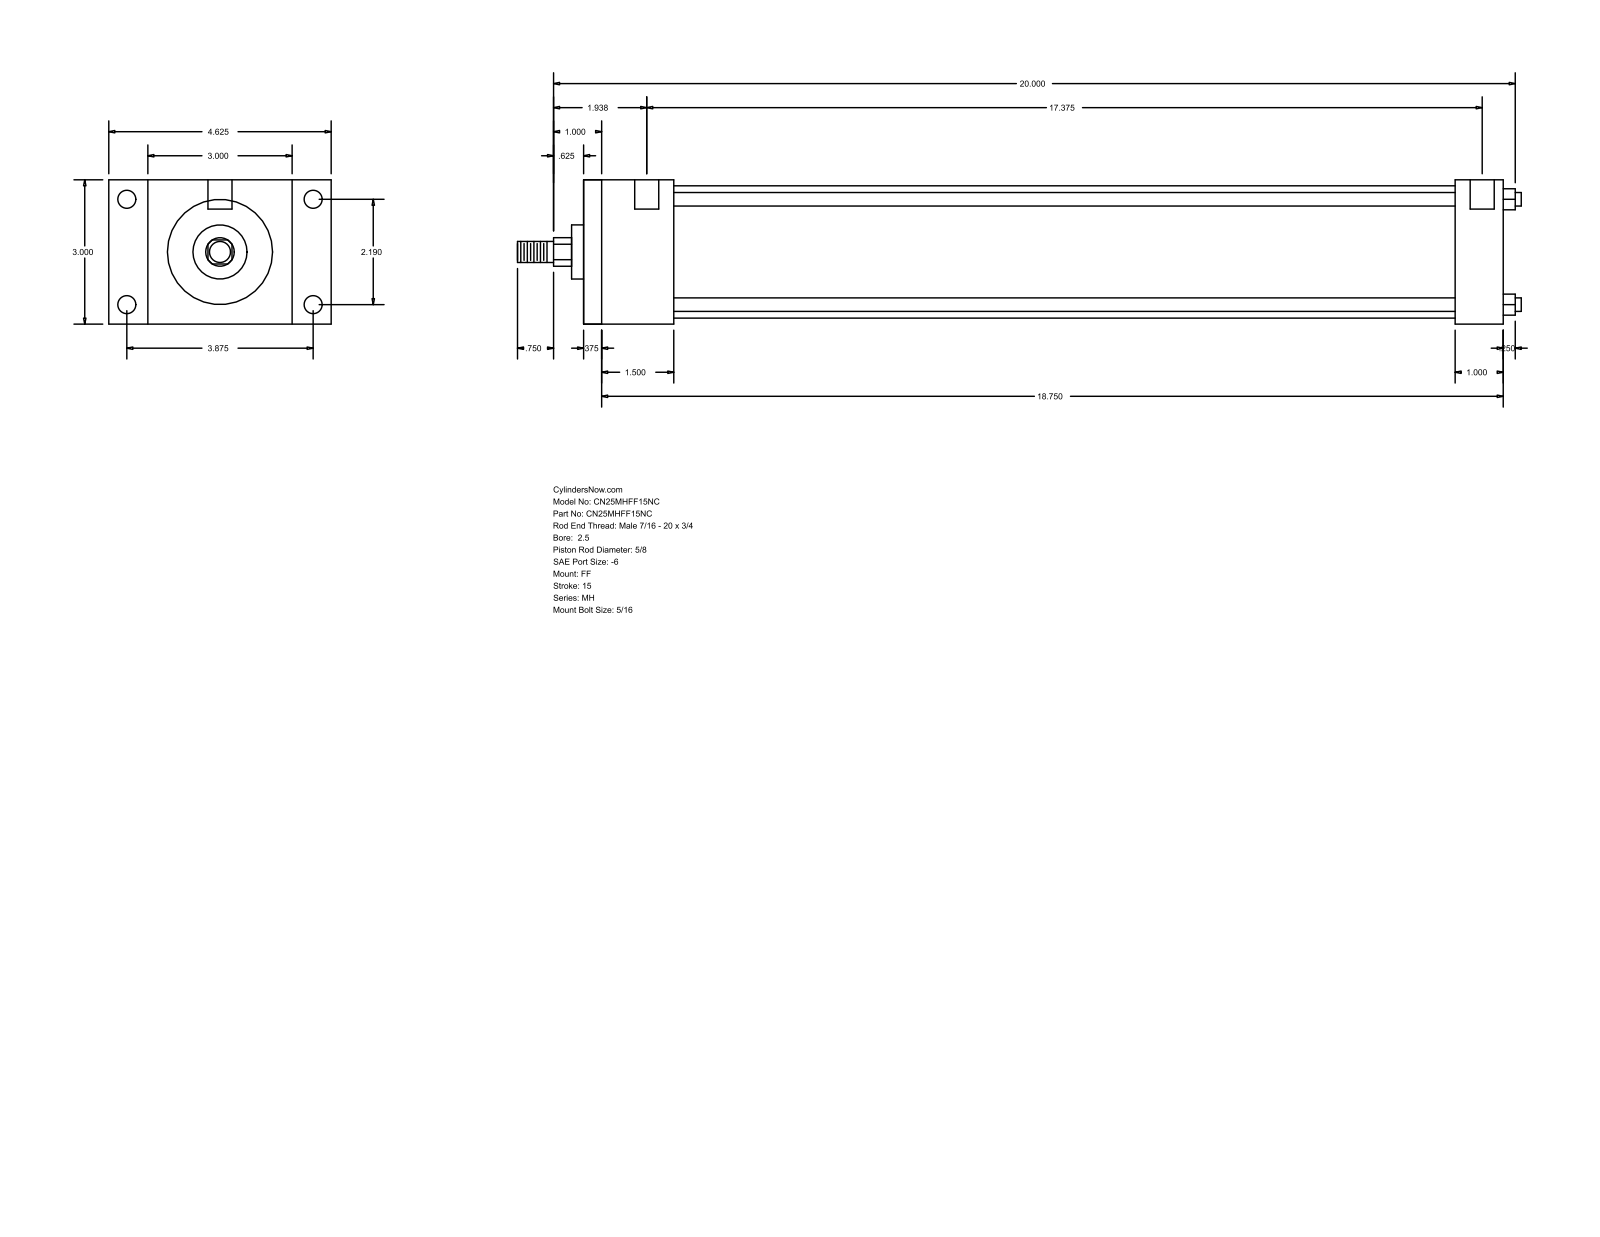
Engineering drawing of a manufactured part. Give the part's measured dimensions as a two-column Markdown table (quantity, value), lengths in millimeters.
| quantity | value |
| --- | --- |
| part name | MH_FF__0250_0.625 |
| STEP written by | GSSL Pune (CONFIG_CONTROL_DESIGN) |
| units | millimeters |
| bodies | 0 solids, 92 faces (64 planar, 28 cylindrical, 0 other) |
| overall size | 530.23 × 117.47 × 76.2 |
| round holes (diameter × count) | 5.56 × 4, 9.53 × 4, 12.7 × 2 |
| round bosses / shafts (diameter × count) | 7.14 × 4, 69.85 × 1, 28.57 × 1, 15.88 × 1, 11.11 × 1 |
| partial cylindrical surfaces (radius × count) | 7.54 × 1 |
| main face-to-face distances | 76.2, 485.77, 476.25, 9.52, 25.4, 47.62, 460.37, 38.1, 450.85, 412.75 |
| hole center spacings | 55.62, 98.42, 113.05, 449.26, 3.17, 4.76, 441.33, 444.5 |
